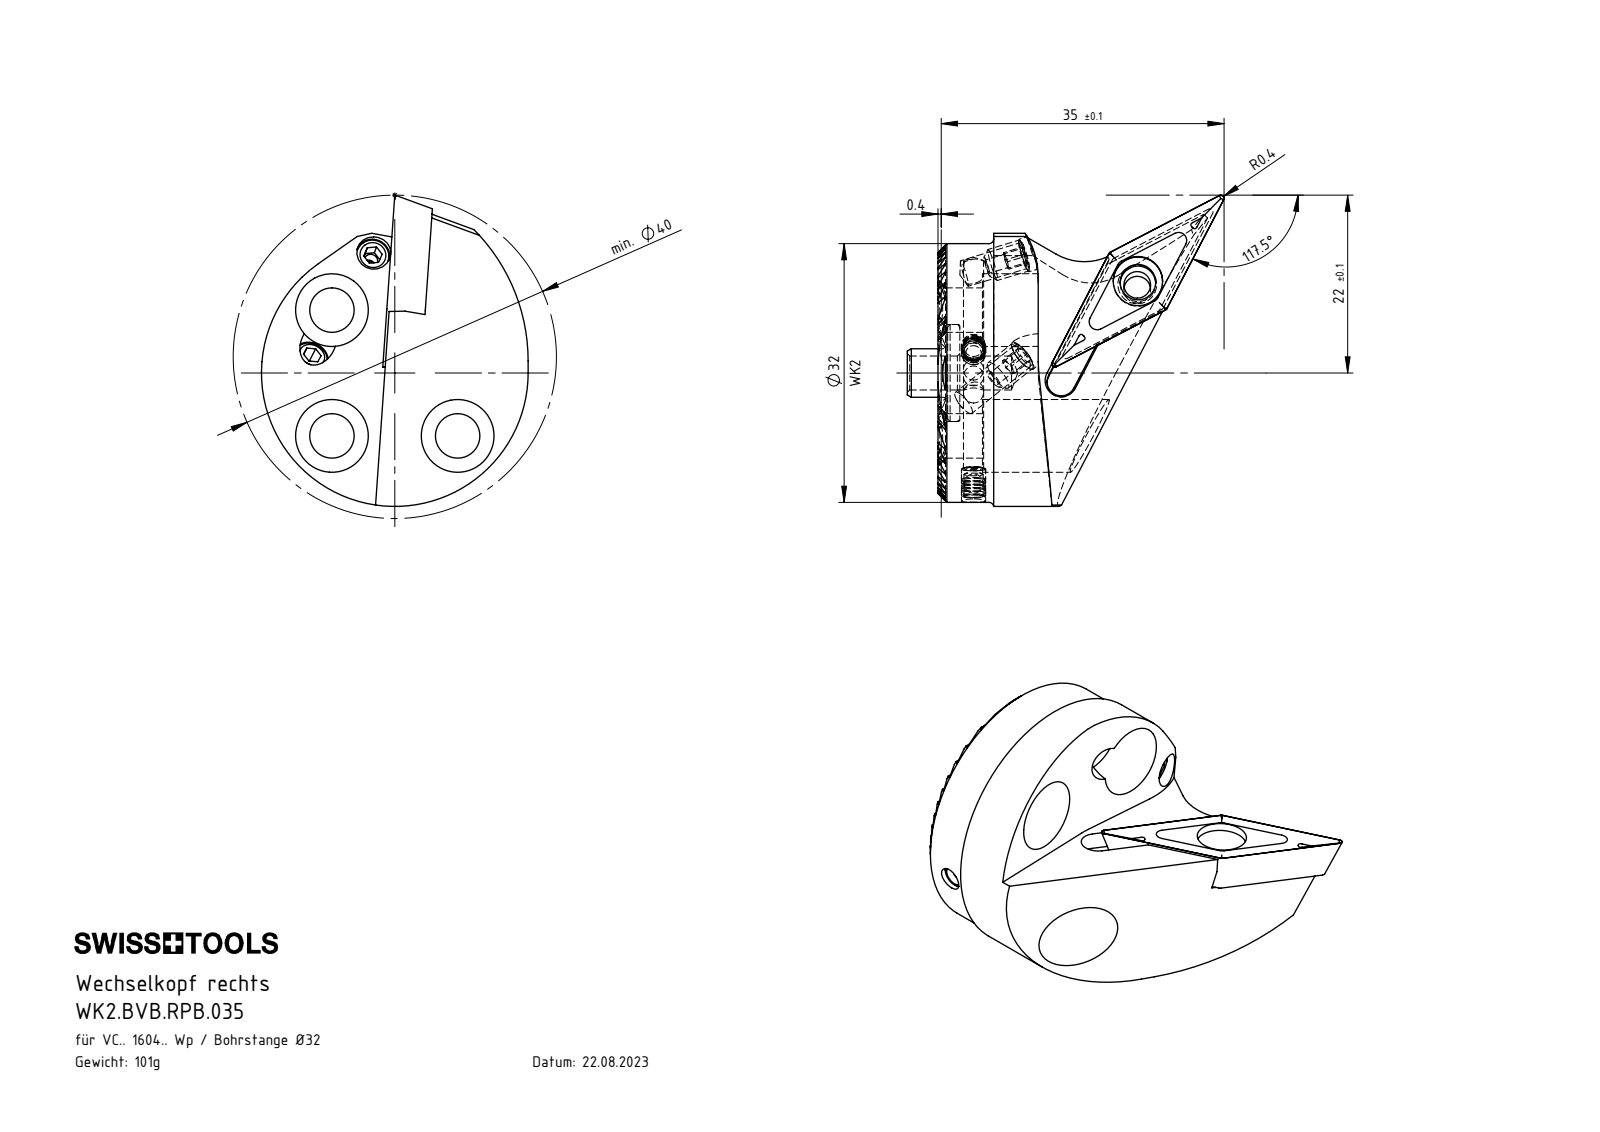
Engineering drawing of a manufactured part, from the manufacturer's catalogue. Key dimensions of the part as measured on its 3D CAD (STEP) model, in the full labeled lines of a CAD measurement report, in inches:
Part name (STEP PRODUCT): WK2.BVB.RPB.035; WKX-ER1.004.005_A_PreviewCfg; WK2-ER1.001.012_A_Fertigbearbeitung; KVT_MB_600_030 (+2 more)
STEP written by: SolidWorks 2017 (AUTOMOTIVE_DESIGN)
Units: inches
Bodies: 9 solids, 358 faces (193 planar, 83 cylindrical, 82 other)
Overall size (bounding box): 1.543 × 1.516 × 1.299
Volume: 0.754 in³ · Surface area: 11.58 in²
Round holes (diameter × count): ⌀0.13 ×3, ⌀0.165 ×3, ⌀0.217 ×3, ⌀0.354 ×3, ⌀0.067 ×2, ⌀0.094 ×2, ⌀0.098 ×2, ⌀0.118 ×2, ⌀0.173 ×1, ⌀0.24 ×1, ⌀0.472 ×1
Round bosses / shafts (diameter × count): ⌀0.157 ×2, ⌀0.118 ×2, ⌀1.26 ×1, ⌀0.236 ×1
Partial cylindrical surfaces — rounded edges, fillets, slot ends (radius × count): R0.005 ×22, R0.472 ×2, R0.069 ×1, R0.276 ×1, R0.65 ×1, R0.906 ×1
Main face-to-face distances: 0.051, 0.102, 0.154, 0.205, 0.256, 0.511, 0.46, 0.563, 0.307, 0.409
Hole centre spacings: 0.433, 0.613, 0.867
